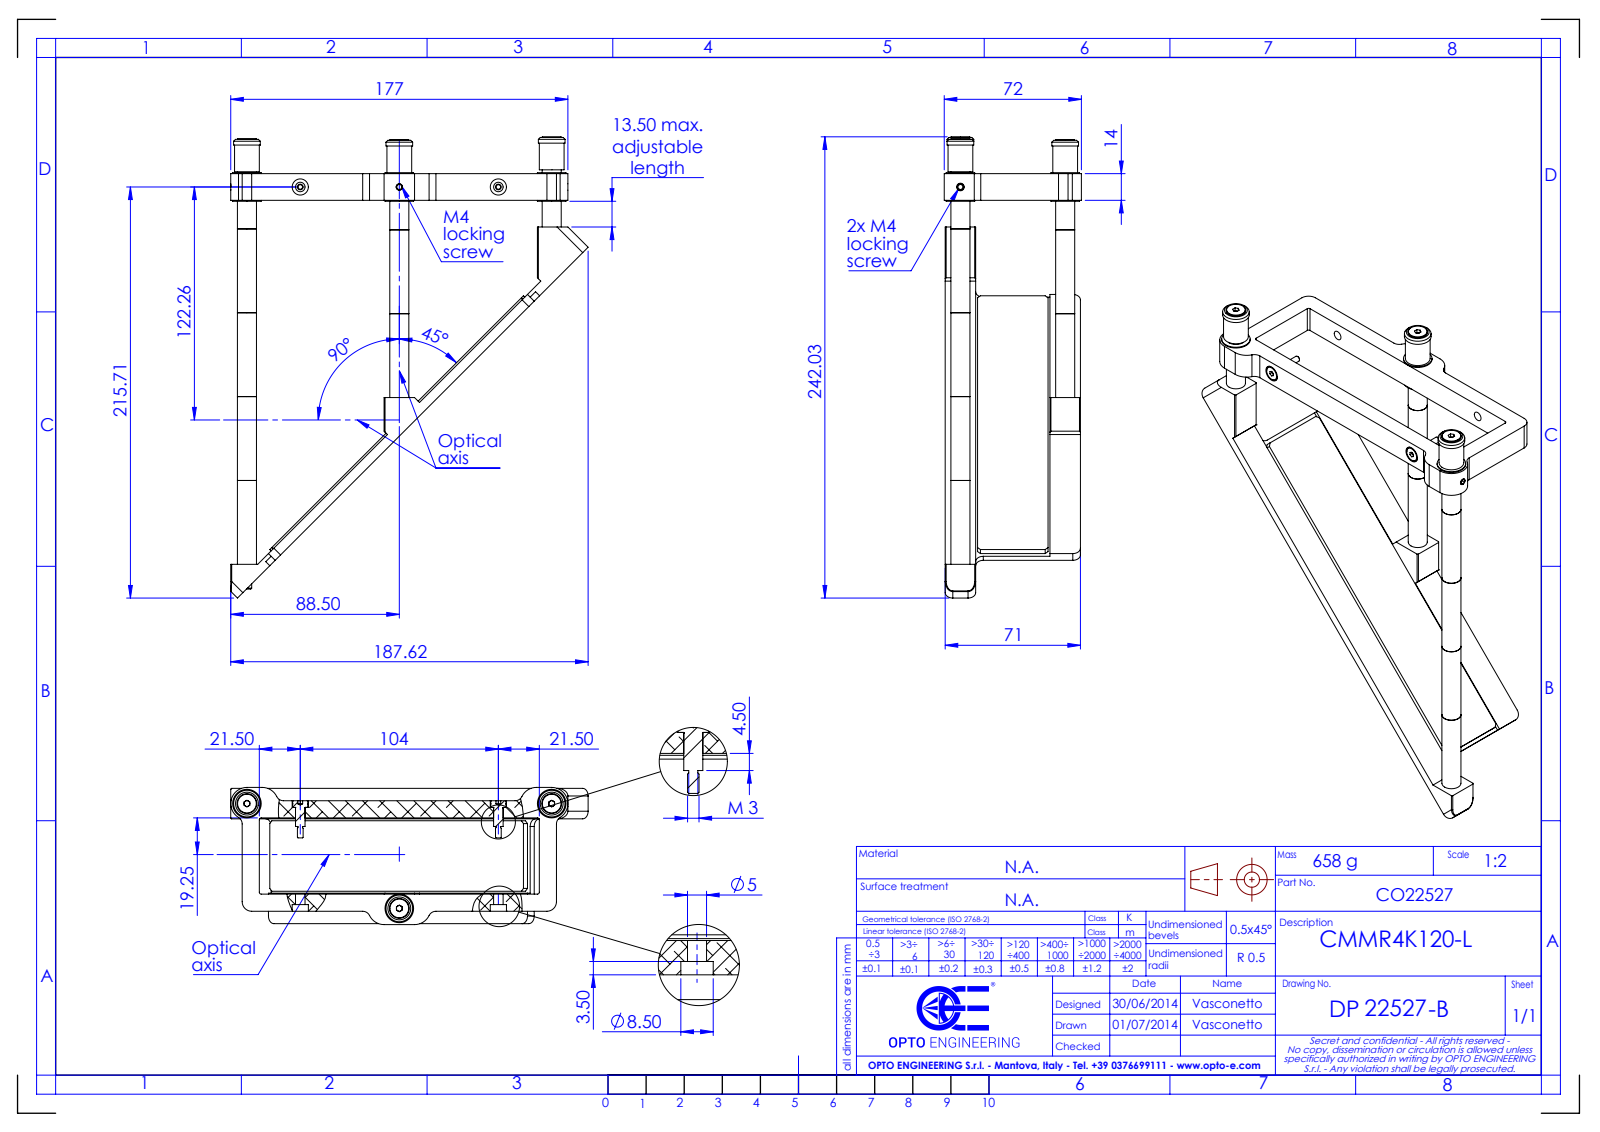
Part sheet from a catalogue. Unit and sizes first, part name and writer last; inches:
Units: inches
Overall size (bounding box): 9.529 × 7.387 × 2.835
Round holes (diameter × count): ⌀0.165 ×3, ⌀0.197 ×2, ⌀0.335 ×2
Round bosses / shafts (diameter × count): ⌀0.591 ×3, ⌀0.551 ×3, ⌀0.512 ×3, ⌀0.394 ×3, ⌀0.388 ×3, ⌀0.118 ×2, ⌀0.094 ×2, ⌀0.315 ×1
Partial cylindrical surfaces — rounded edges, fillets, slot ends (radius × count): R0.157 ×14, R0.335 ×6, R0.039 ×4, R0.197 ×2
Main face-to-face distances: 0.118, 0.039, 0.236, 0.079, 0.197, 0.551, 0.354, 2.185, 1.929, 0.61
Hole centre spacings: 3.822, 4.094, 6.299
Bodies: 0 solids, 268 faces (128 planar, 108 cylindrical, 32 other)
Part name (STEP PRODUCT): DP22527-B_CMMR4K120-L
STEP written by: SolidWorks 2021 (CONFIG_CONTROL_DESIGN)
